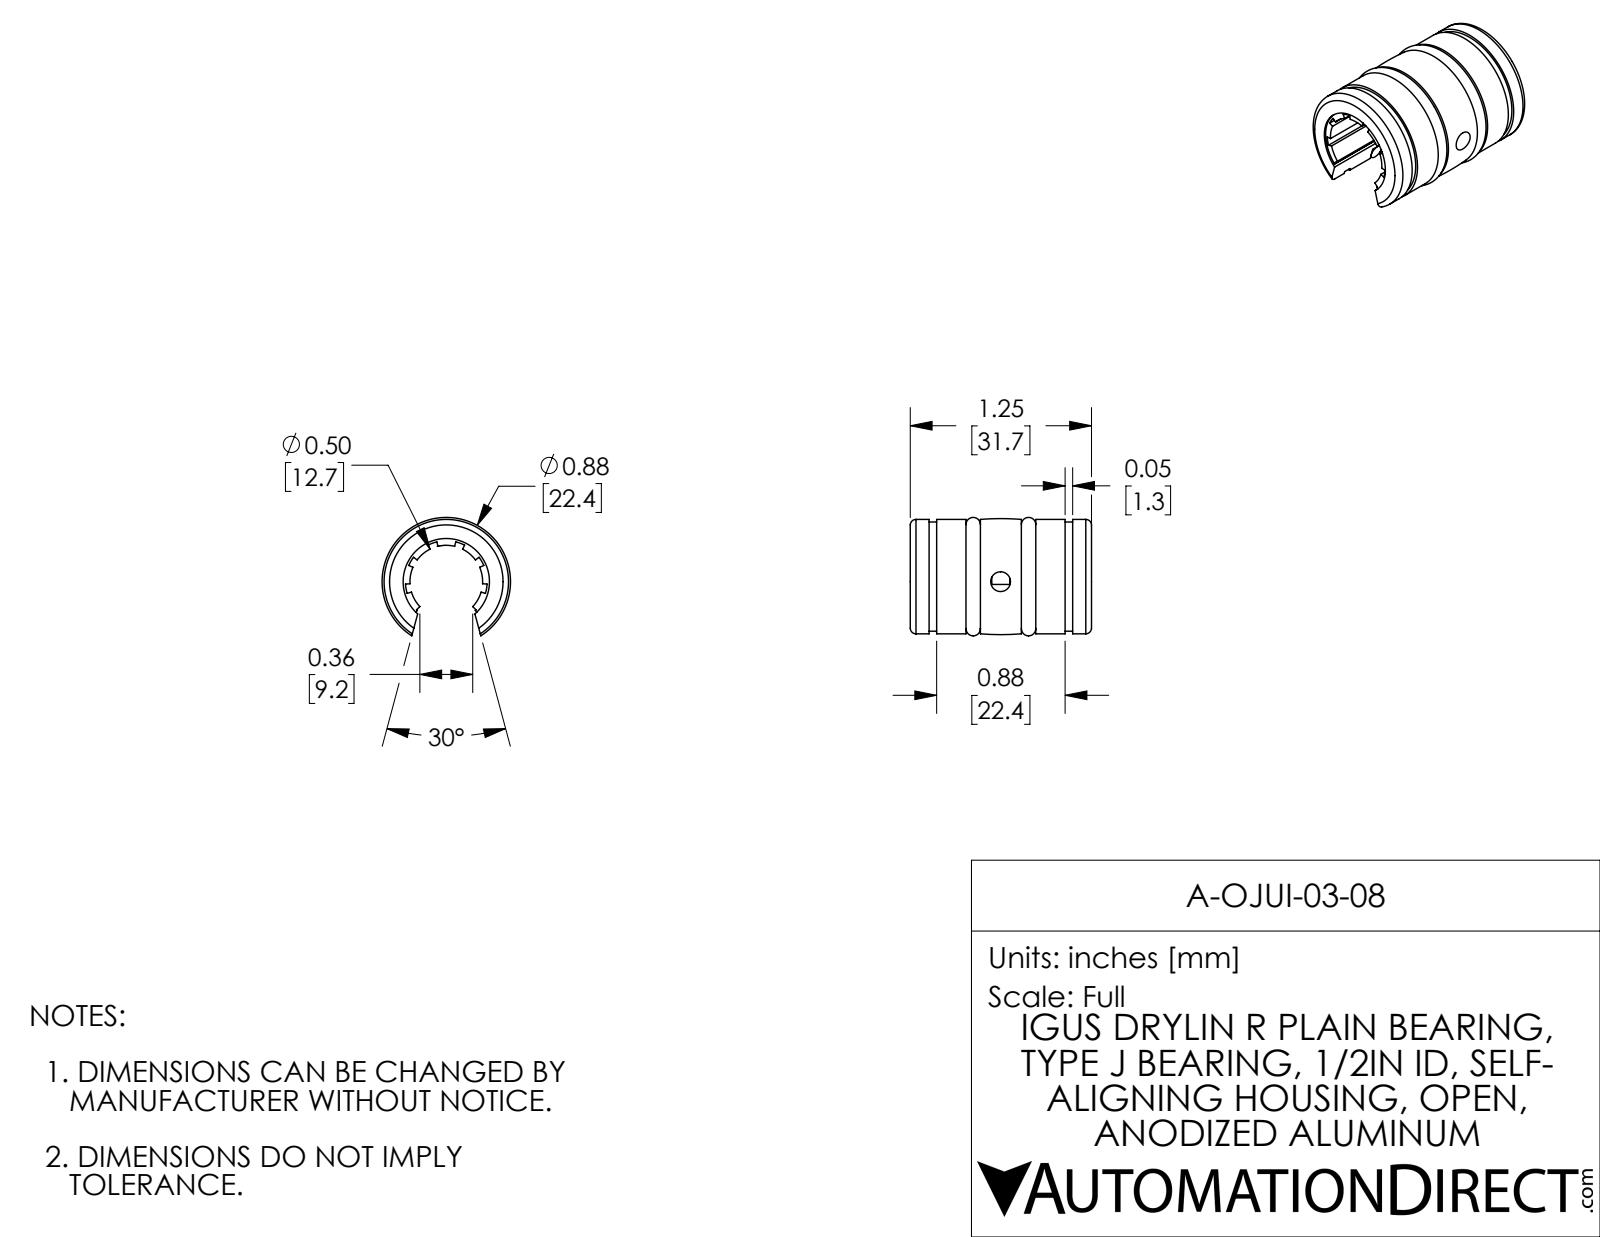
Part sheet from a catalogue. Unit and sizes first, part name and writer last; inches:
Units: inches
Overall size (bounding box): 1.246 × 0.883 × 0.814
Round holes (diameter × count): ⌀0.136 ×1
Round bosses / shafts (diameter × count): ⌀0.856 ×1, ⌀0.82 ×1, ⌀0.102 ×1
Partial cylindrical surfaces — rounded edges, fillets, slot ends (radius × count): R0.25 ×1, R0.281 ×1, R0.297 ×1, R0.328 ×1, R0.336 ×1, R0.342 ×1
Main face-to-face distances: 0.099, 0.38, 0.383, 0.483, 0.764, 0.863, 0.561, 0.686, 0.177, 0.302
Volume: 0.346 in³ · Surface area: 11.38 in²
Bodies: 4 solids, 127 faces (67 planar, 39 cylindrical, 21 other)
Part name (STEP PRODUCT): A-OJUI-03-08
STEP written by: SolidWorks 2017 (AUTOMOTIVE_DESIGN)
